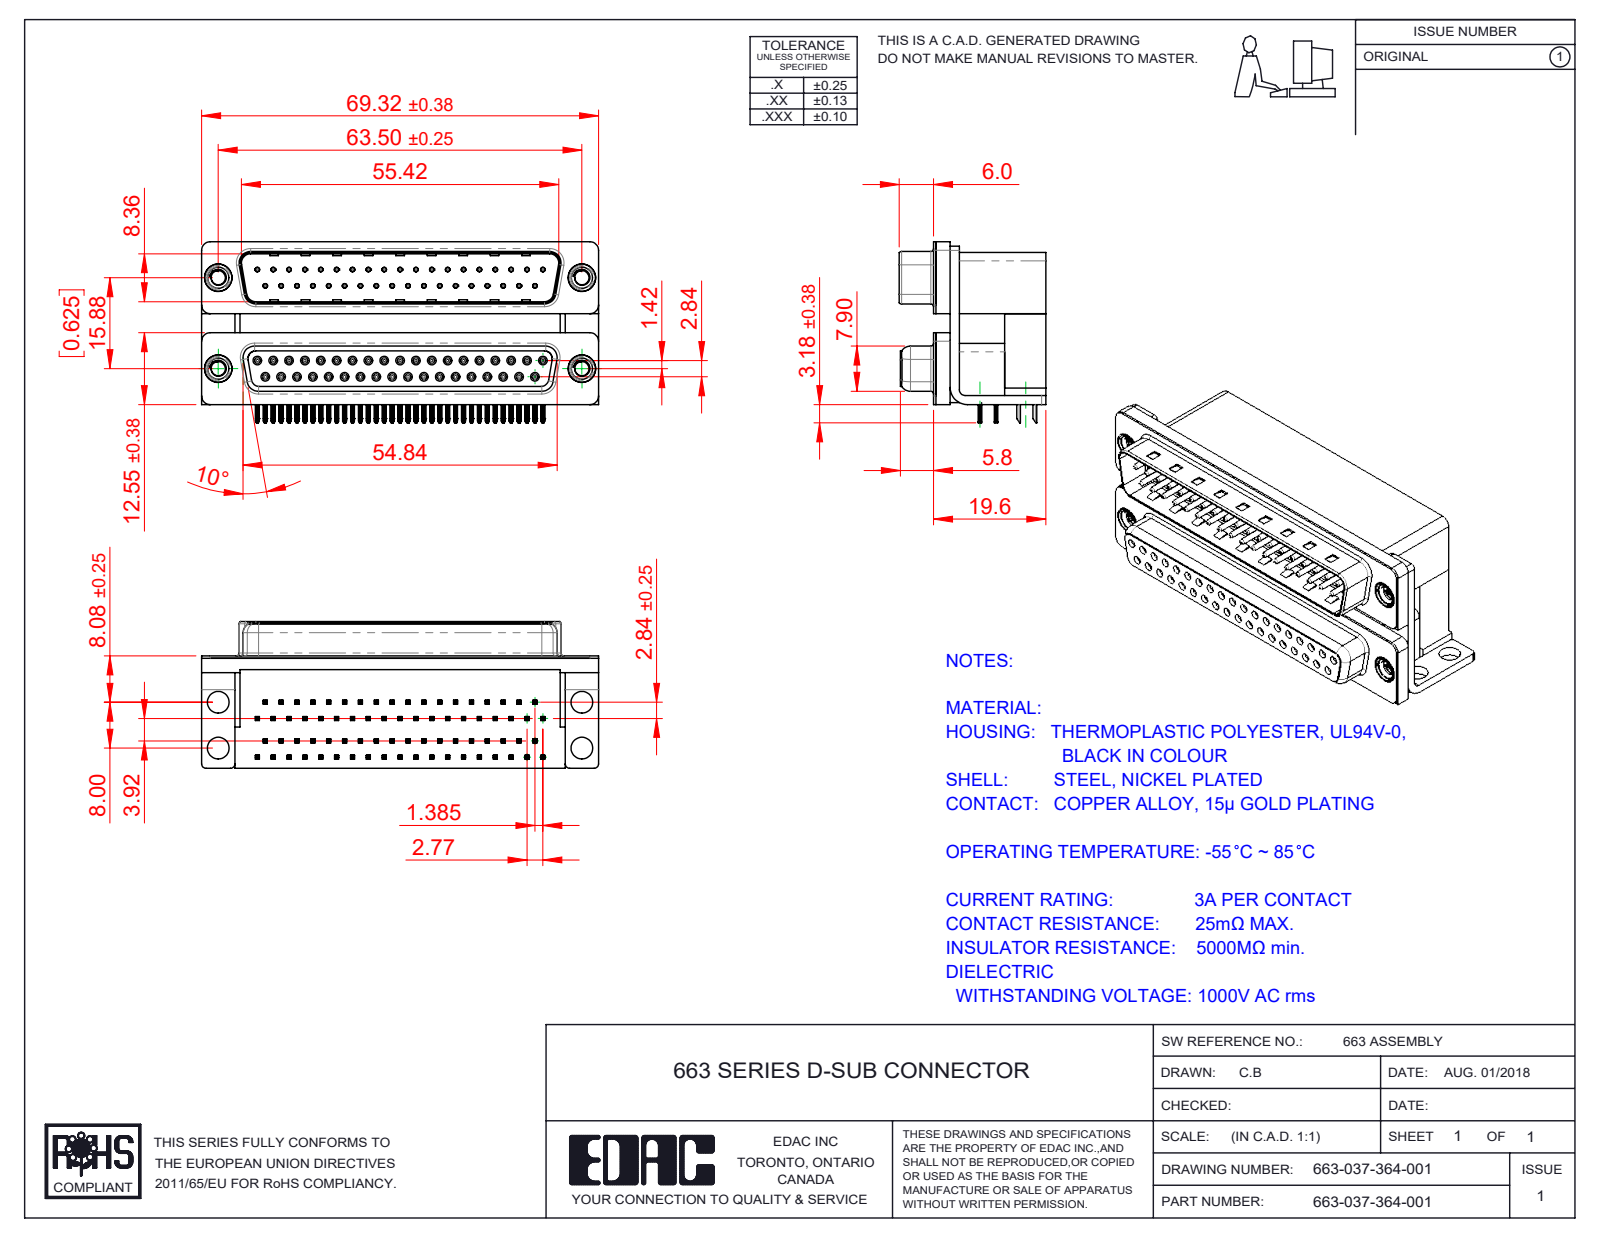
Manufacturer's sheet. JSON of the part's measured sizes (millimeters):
{"part_name": "663 Shell Receptacle_37 Contacts; 663 Contact Top Upper_L; 663 Contact Bottom Upper_L; 663 Mounting Bracket_NoneL (+8 more)", "step_written_by": "SolidWorks 2020 (CONFIG_CONTROL_DESIGN)", "units": "millimeters", "bodies": {"solids": 85, "faces": 8949, "planar": 4741, "cylindrical": 2185, "other": 2023}, "overall_size": [69.32, 31.61, 25.6], "volume_mm3": 29878, "surface_area_mm2": 31156, "round_holes": [[0.8, 74], [0.35, 37], [0.9, 37], [2.5, 4], [3.5, 4], [3.8, 4], [4, 4], [4.8, 4], [5, 4]], "round_bosses_or_shafts": [[1.2, 37], [0.75, 37], [4.9, 4], [4.75, 4], [3.9, 4]], "partial_cylinders_radius": [[0.1, 296], [0.15, 148], [0.25, 148], [0.12, 74], [0.35, 74], [0.34, 37], [0.28, 18], [1.5, 13]], "face_to_face_distances": [0.4, 19.2, 7.2, 12, 15.52, 26.22, 10.7, 2.84, 16.7, 9.5], "hole_center_spacings": [3.16, 2.77, 5.54, 8.31, 11.08, 13.85, 16.62, 19.39]}
